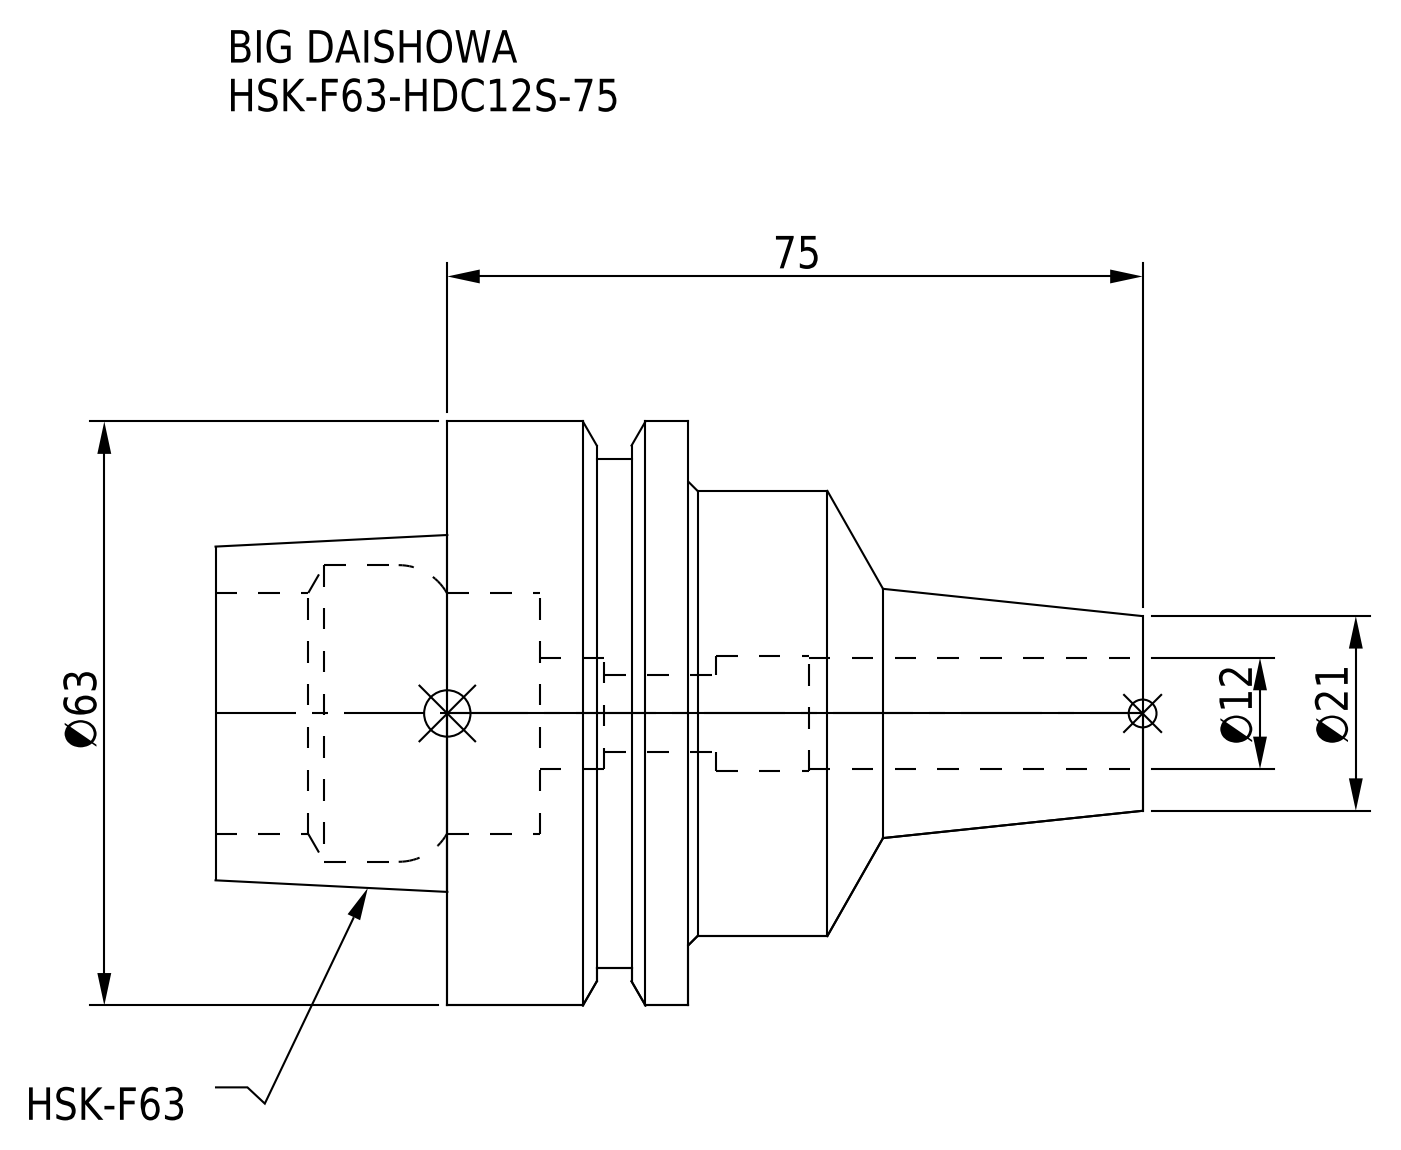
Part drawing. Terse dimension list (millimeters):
name: HSK-F63-HDC12S-75
written by: CREO PARAMETRIC BY PTC INC, 2016380 (AUTOMOTIVE_DESIGN)
unit: mm
bodies: 1 solid, 50 faces (10 planar, 24 cylindrical, 16 other)
size: 100 × 63 × 63
volume: 122 742 mm³; area: 24 953 mm²
holes: 1× ⌀8.25, 1× ⌀12, 1× ⌀12.5, 1× ⌀26, 1× ⌀32
bosses: 1× ⌀63, 1× ⌀55, 1× ⌀48
face distances: 26, 51, 25, 16.05, 9.95, 34.95, 6.12, 9.93, 19.88, 44.88
